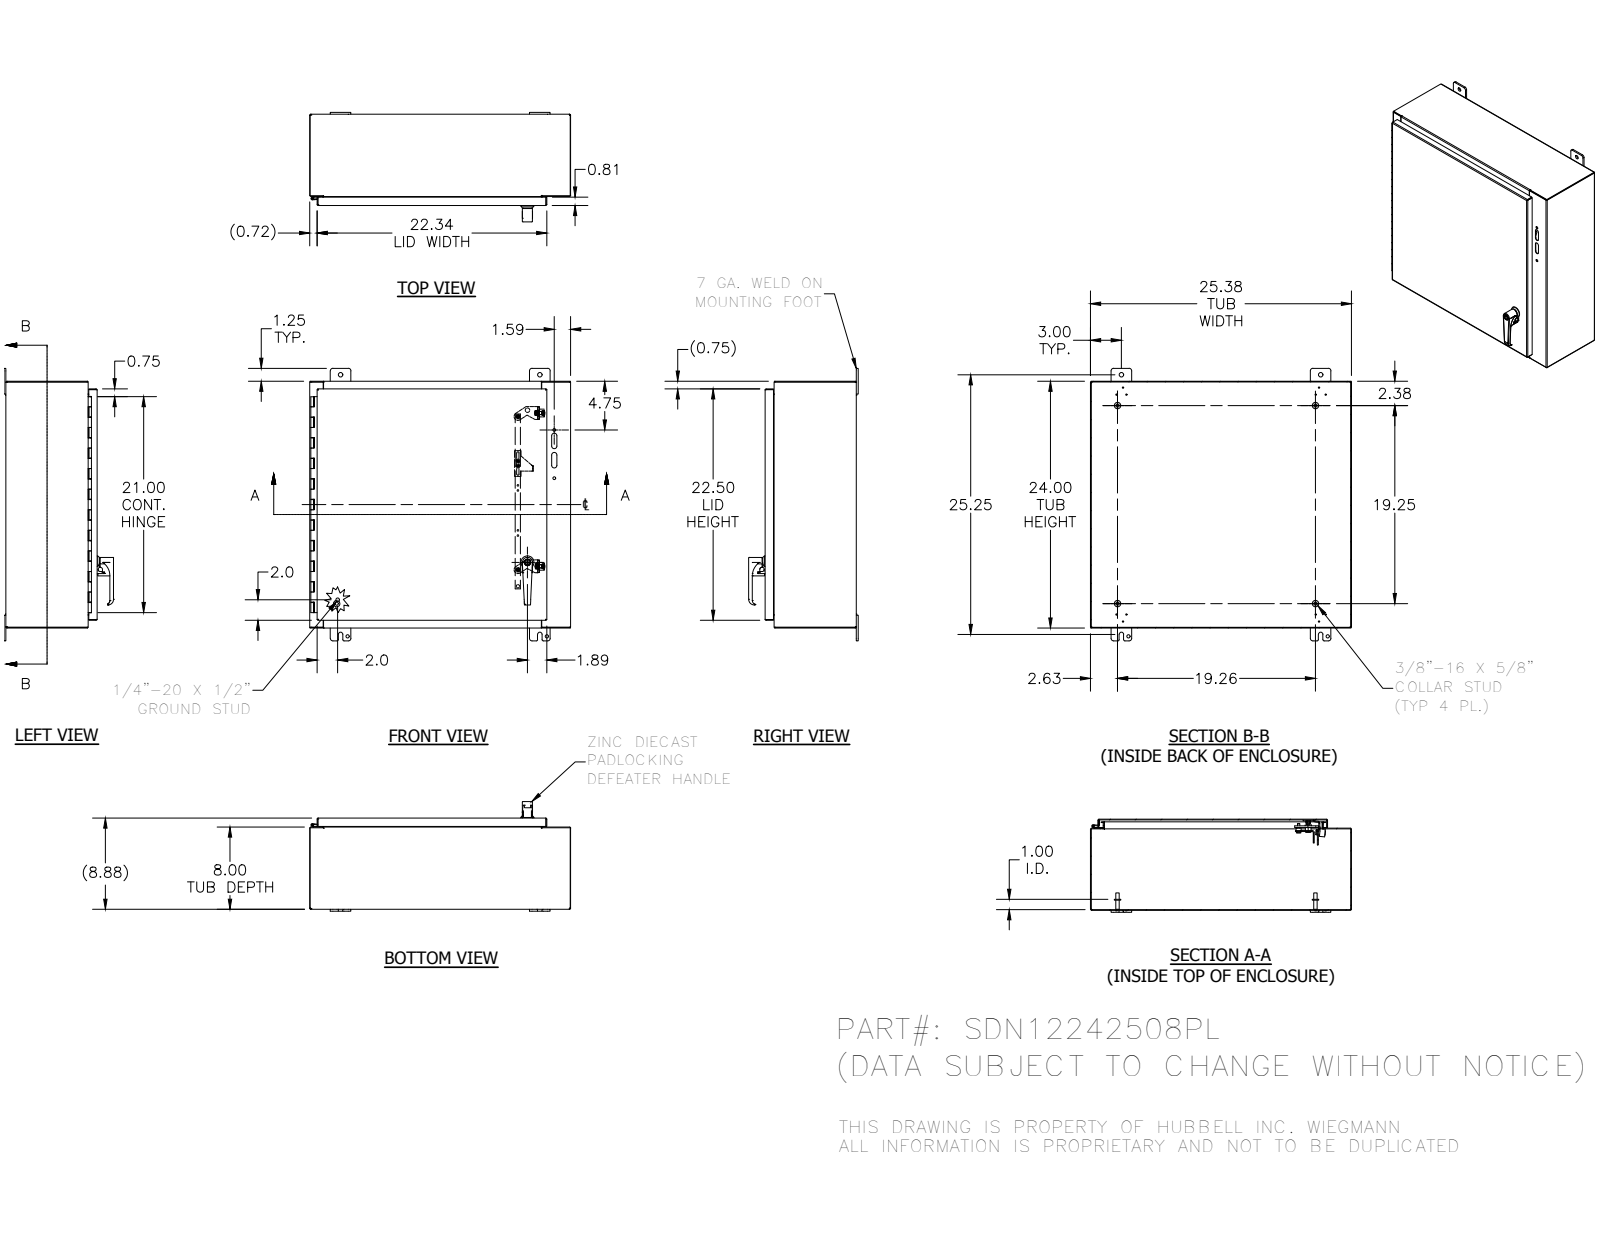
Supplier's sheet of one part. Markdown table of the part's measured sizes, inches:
| quantity | value |
| --- | --- |
| part name | SDN12242508PL |
| STEP written by | SolidWorks 2019 (AUTOMOTIVE_DESIGN) |
| units | inches |
| bodies | 49 solids, 1545 faces (792 planar, 525 cylindrical, 228 other) |
| overall size | 26.5 × 25.38 × 10.649 |
| volume | 173.5 in³ |
| surface area | 4 619 in² |
| round holes (diameter × count) | 0.12 × 12, 0.145 × 6, 0.313 × 4, 0.438 × 4, 0.32 × 3, 0.156 × 2, 0.196 × 2, 0.211 × 2, 0.22 × 2, 0.281 × 2, 0.313 × 2, 0.45 × 2 |
| round bosses / shafts (diameter × count) | 0.33 × 5, 0.625 × 4, 0.437 × 4, 0.3 × 4, 0.25 × 4, 0.19 × 4, 0.225 × 3, 0.75 × 2 |
| partial cylindrical surfaces (radius × count) | 0.02 × 38, 0.012 × 31, 0.25 × 22, 0.031 × 20, 0.105 × 20, 0.125 × 17, 0.025 × 16, 0.07 × 8 |
| main face-to-face distances | 0.074, 8.801, 8.727, 8.875, 23.926, 25.306, 7.926, 0.875, 24, 23.852 |
| hole center spacings | 14.9, 0.759, 1.593, 18.749, 19.38, 21.38, 21.402, 22.068 |
